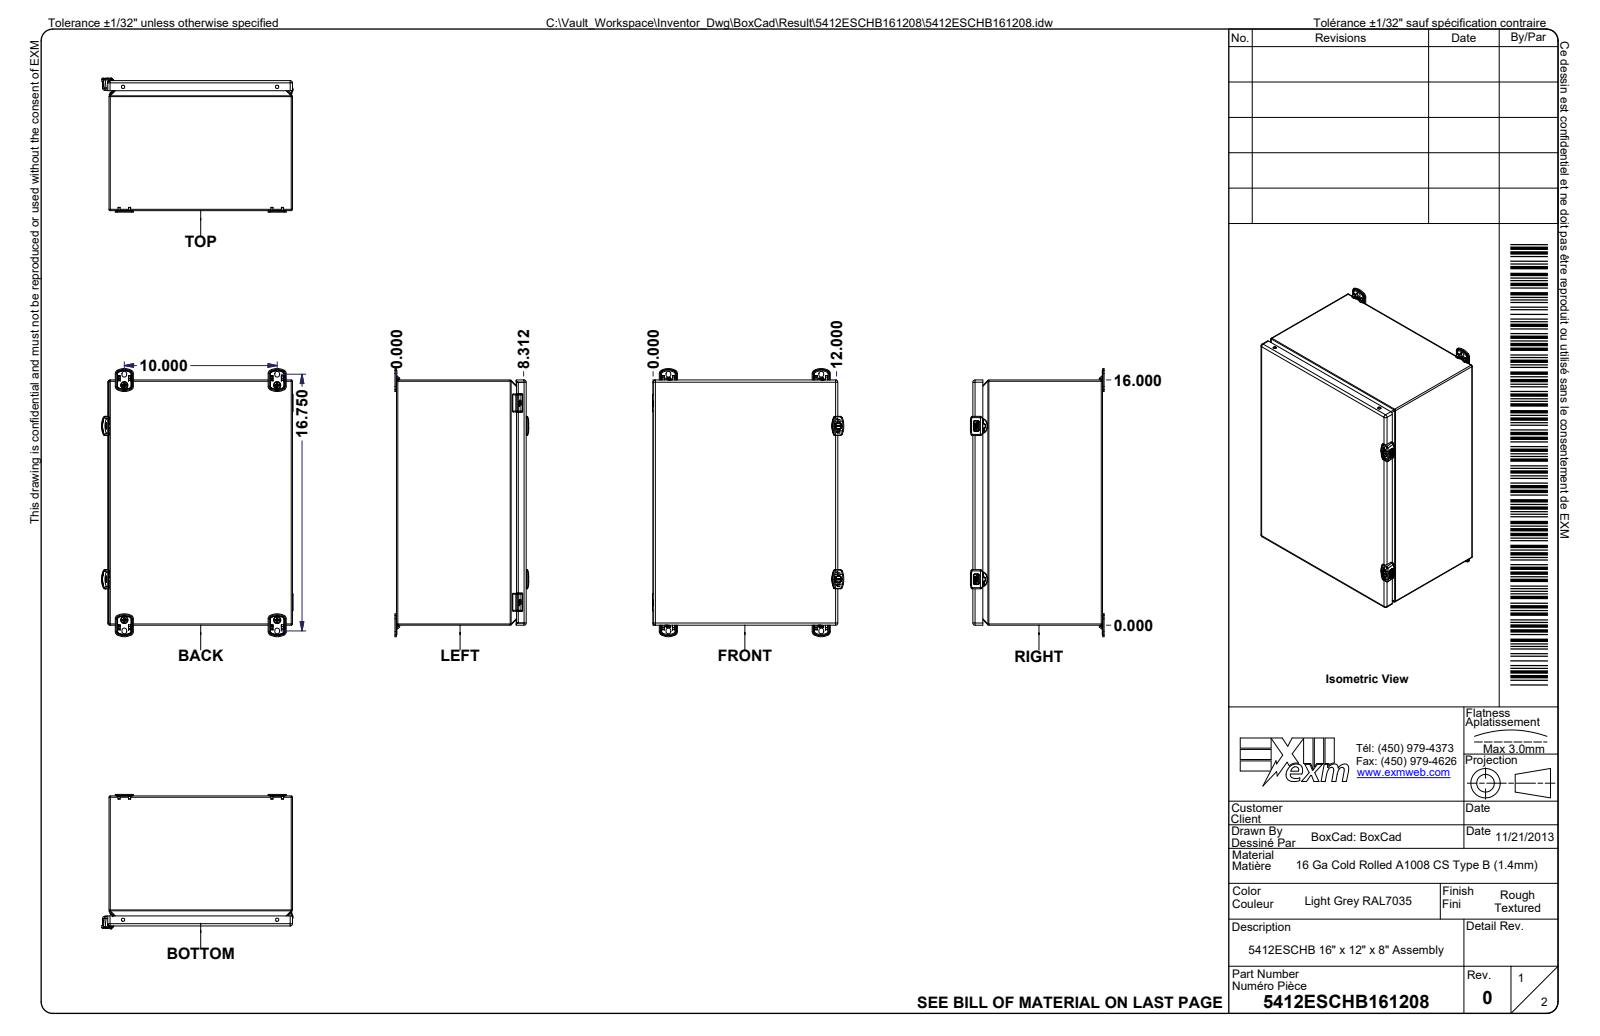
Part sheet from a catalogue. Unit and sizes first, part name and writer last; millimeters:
Units: millimetres
Overall size (bounding box): 444.4 × 316 × 221.9
Round holes (diameter × count): ⌀5.1 ×11, ⌀0.8 ×6, ⌀6.1 ×6, ⌀7.7 ×4, ⌀7.9 ×4, ⌀8.1 ×4, ⌀4.2 ×2, ⌀4.4 ×2, ⌀4.4 ×2, ⌀5.5 ×2, ⌀6 ×2, ⌀10 ×2
Round bosses / shafts (diameter × count): ⌀5.9 ×8, ⌀0.9 ×6, ⌀13 ×4, ⌀9.9 ×4, ⌀5 ×3, ⌀10.5 ×2, ⌀10 ×2, ⌀8.4 ×2
Partial cylindrical surfaces — rounded edges, fillets, slot ends (radius × count): R0.2 ×226, R0.5 ×179, R0.1 ×98, R1 ×83, R0.3 ×49, R0.3 ×43, R0.6 ×33, R0.8 ×33
Main face-to-face distances: 1.3, 214.1, 303.5, 212.7, 405.1, 215.4, 13.6, 12.2, 10.5, 202.2
Hole centre spacings: 257.5, 260.4, 13.9, 375.4, 455.1, 254, 289.8, 419.4
Volume: 1 034 000 mm³ · Surface area: 1 454 000 mm²
Bodies: 57 solids, 8149 faces (3851 planar, 1834 cylindrical, 2464 other)
Part name (STEP PRODUCT): 5412ESCHB161208; 5412ESCHB161208B; 5412ESCHB161208B-P; STK-Q-08350 (+8 more)
STEP written by: Autodesk Inventor 2024 (AUTOMOTIVE_DESIGN)
